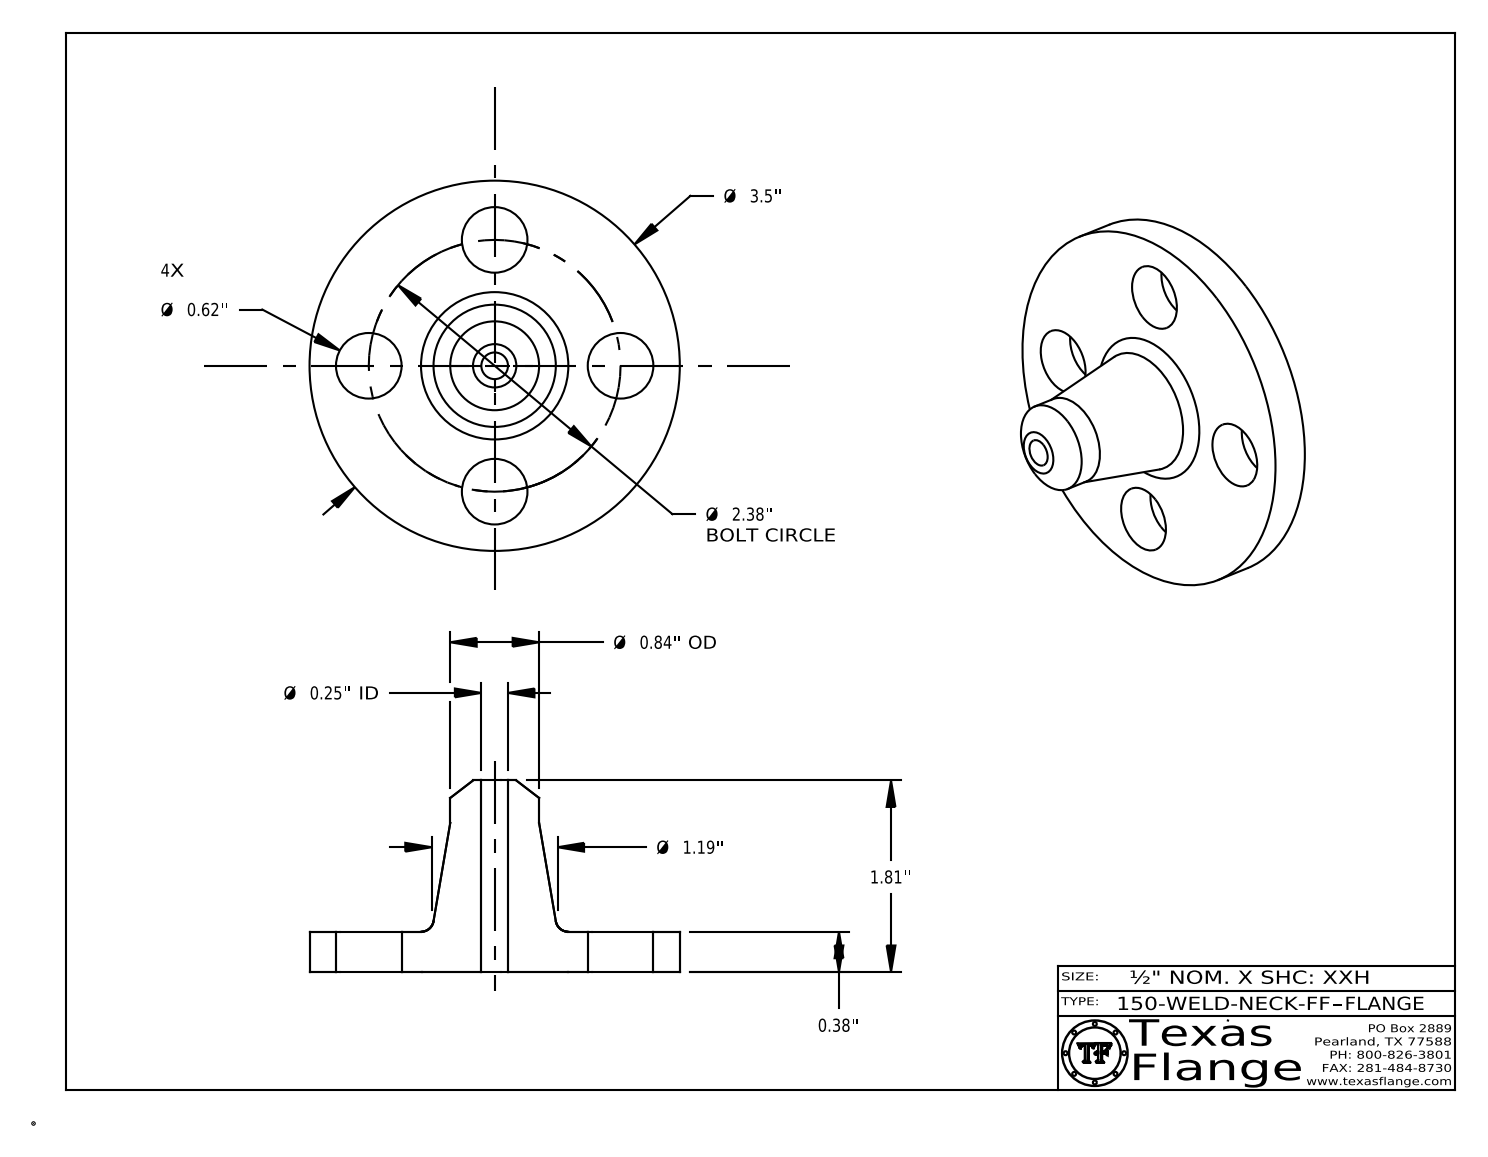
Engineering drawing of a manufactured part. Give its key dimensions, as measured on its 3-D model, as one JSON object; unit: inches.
{"part_name": "150-WELD-NECK-FF", "step_written_by": "CATIA V5 STEP AP214 (AUTOMOTIVE_DESIGN)", "units": "inches", "bodies": {"solids": 1, "faces": 409, "planar": 369, "cylindrical": 34, "other": 6}, "overall_size": [3.5, 3.5, 1.81], "volume_in3": 4.138, "surface_area_in2": 28.77, "round_holes": [[0.62, 4], [0.252, 1], [0.495, 1]], "round_bosses_or_shafts": [[0.03, 8], [3.5, 1], [0.84, 1], [0.39, 1]], "face_to_face_distances": [0.38, 1.81, 1.43, 0.365, 0.015, 1.445, 0.148, 0.145, 0.027, 0.096], "hole_center_spacings": [1.19, 1.683, 0.911, 2.199, 2.38, 1.19]}
